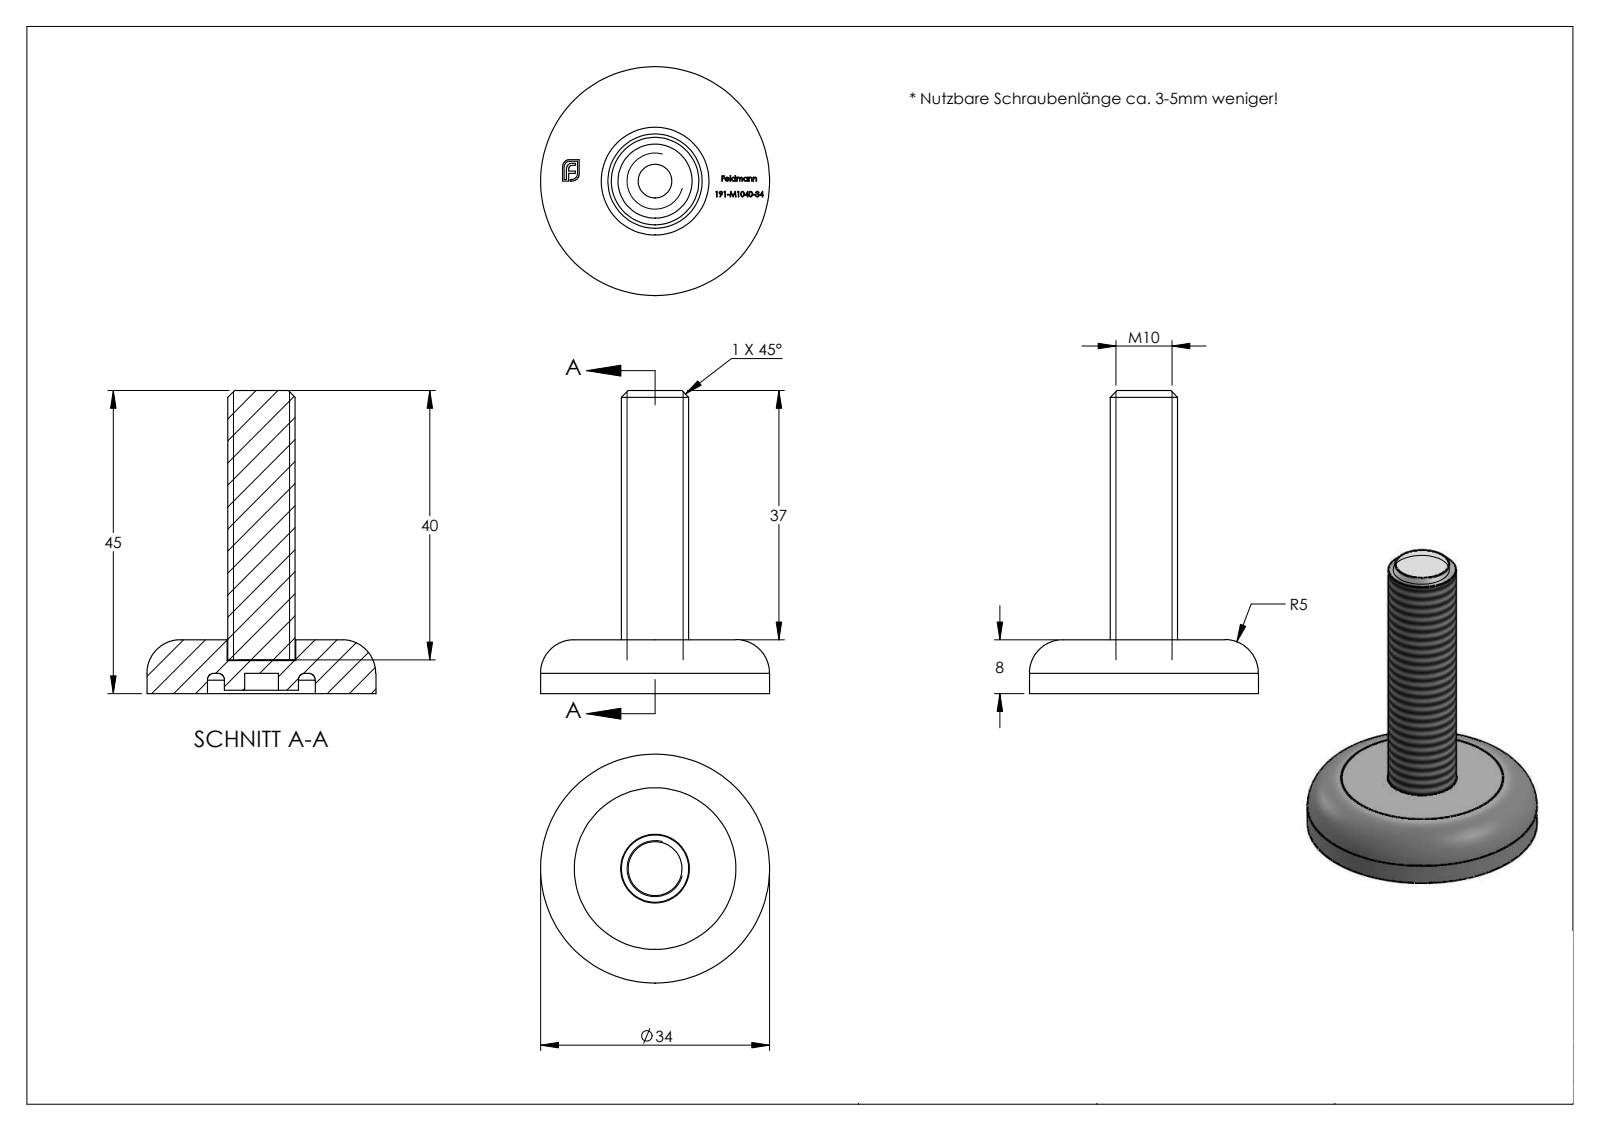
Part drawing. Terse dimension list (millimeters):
name: 191-M1040-34
written by: SolidWorks 2018 (CONFIG_CONTROL_DESIGN)
unit: mm
bodies: 2 solids, 311 faces (182 planar, 12 cylindrical, 117 other)
size: 45 × 34 × 34
volume: 9 204 mm³; area: 4 172 mm²
holes: 1× ⌀5, 1× ⌀10.2, 1× ⌀16
bosses: 1× ⌀34, 1× ⌀11, 1× ⌀10
face distances: 8, 3, 5, 4.9, 3.1, 0.5, 4.4, 4.5, 7.5, 45
